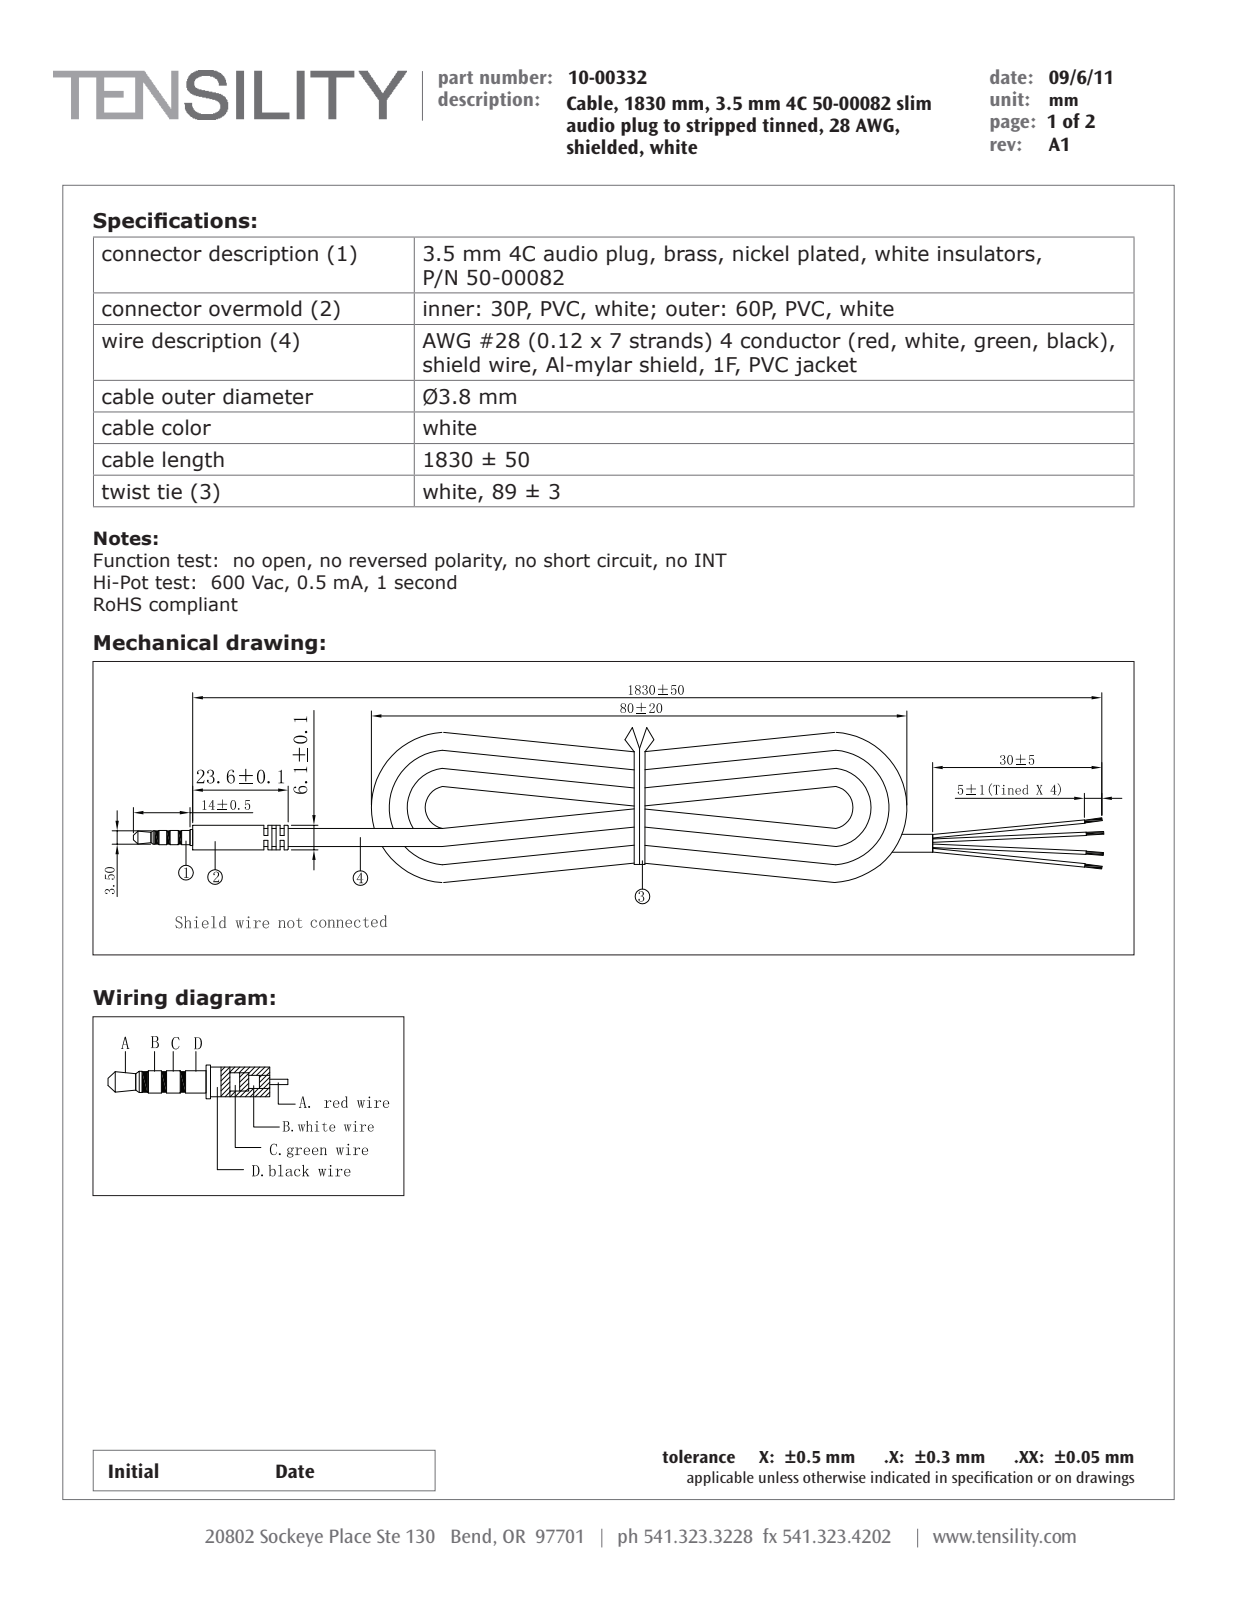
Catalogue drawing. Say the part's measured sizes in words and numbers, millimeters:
The part is named "10-00332_revA4; 50-00403; 24-00028; 30-00181_no heat shrink, no shield". Its 3-D file was written by "SolidWorks 2015 (CONFIG_CONTROL_DESIGN)". It is 124 solids with 814 faces: 310 planar, 458 cylindrical and 46 other. Overall it measures 212.4 by 6.85 by 6.1 millimeters. Its volume is 2 523 cubic millimeters and its surface area 20 097 square millimeters. Round holes: 4 of diameter 0.85, 1 of diameter 2.09, 1 of diameter 2.14. Round bosses or shafts: 1 of diameter 6.1, 1 of diameter 5.8, 1 of diameter 4.5, 1 of diameter 3.8, 1 of diameter 3.53, 1 of diameter 3.52, 1 of diameter 3.5, 1 of diameter 3.49. Partial cylindrical surfaces (rounded edges, fillets, slot ends): 1 of radius 0.94, 1 of radius 0.95. The main face-to-face distances are 0.9, 1.8, 2.7, 3.6, 4.5, 17.9, 5.4, 23.3, 18.8, 22.4. The hole center spacings are 1.14, 0.52, 0.64, 0.39, 0.89, 0.77, 1.01, 1.23.
